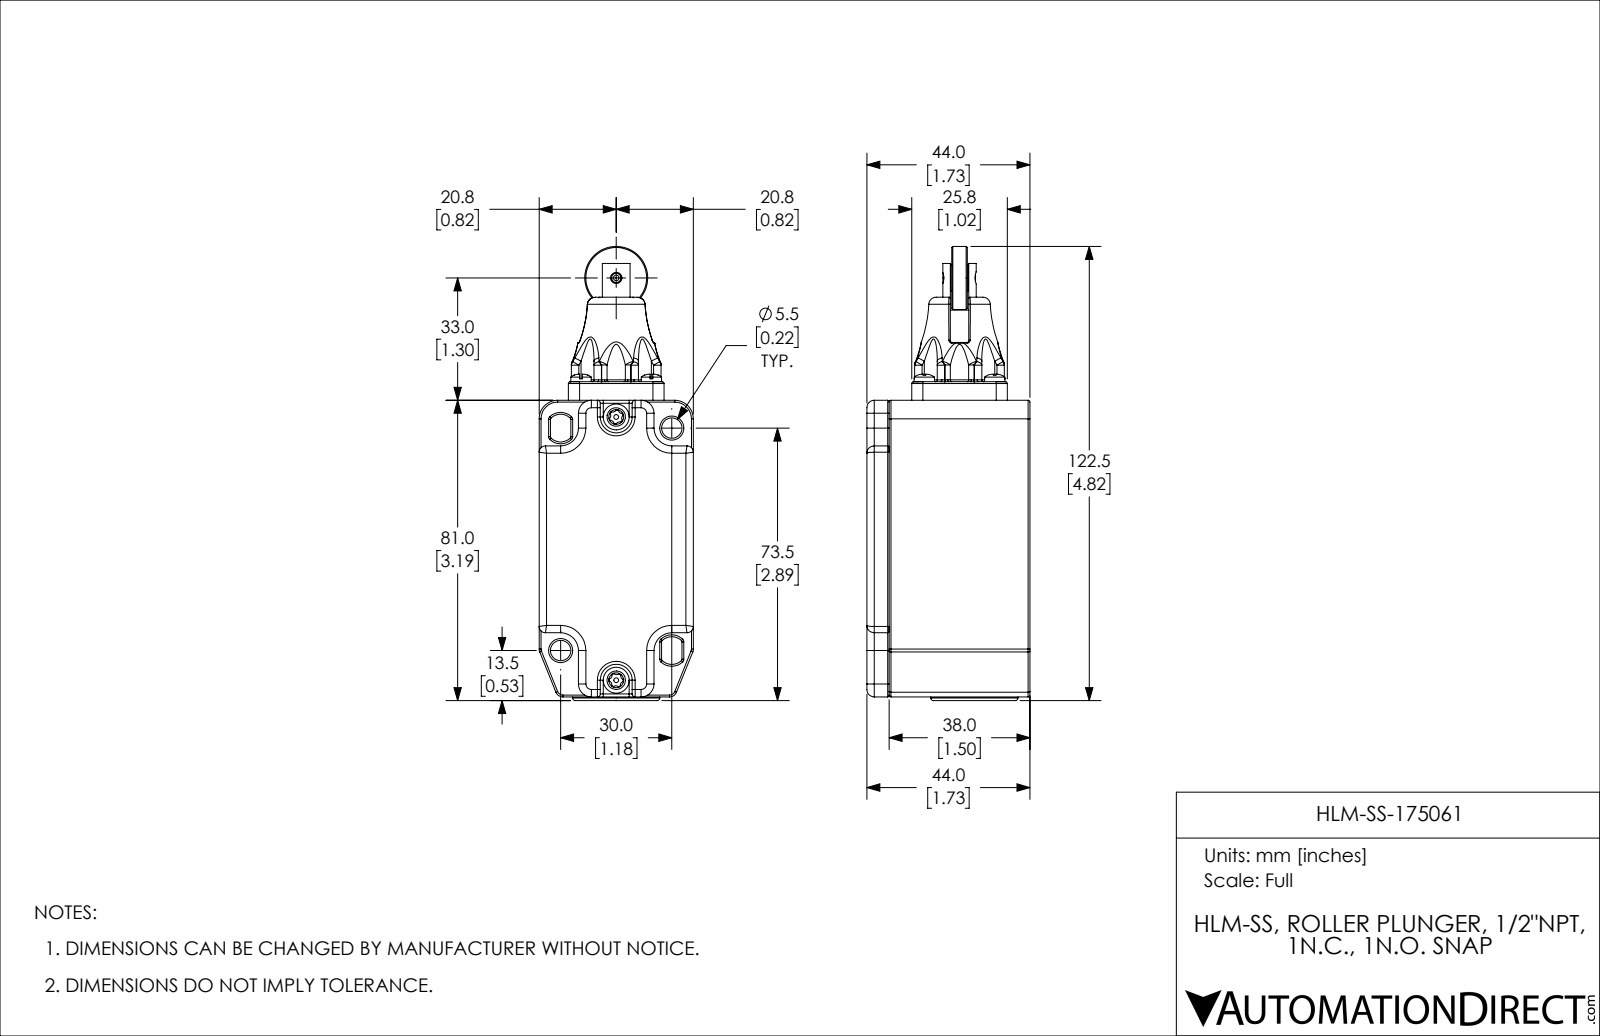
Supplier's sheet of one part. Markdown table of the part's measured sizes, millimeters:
| quantity | value |
| --- | --- |
| part name | 175-HLM-SS (Roller Plunger) (step format) |
| STEP written by | SolidWorks 2013 (CONFIG_CONTROL_DESIGN) |
| units | millimeters |
| bodies | 14 solids, 1997 faces (511 planar, 513 cylindrical, 973 other) |
| overall size | 122.5 × 44 × 41.6 |
| volume | 69 539 mm³ |
| surface area | 45 821 mm² |
| round holes (diameter × count) | 2.6 × 10, 3.3 × 5, 3.4 × 2, 4 × 2, 4.1 × 2, 5.5 × 2, 1.5 × 1, 2.5 × 1, 2.9 × 1, 4.4 × 1, 5.3 × 1, 5.6 × 1 |
| round bosses / shafts (diameter × count) | 6 × 6, 5.48 × 4, 3 × 4, 7 × 3, 1.3 × 2, 23.5 × 1, 18.6 × 1, 17.7 × 1 |
| partial cylindrical surfaces (radius × count) | 0.5 × 126, 2 × 28, 0.4 × 24, 1 × 17, 0.15 × 14, 0.3 × 14, 0.8 × 12, 3.5 × 8 |
| main face-to-face distances | 3.05, 38.55, 35.5, 41.6, 44, 6, 2.5, 41.5, 38, 2.2 |
| hole center spacings | 19, 13.44, 9, 10.98, 16.51, 19.04, 21.02, 21.69 |
